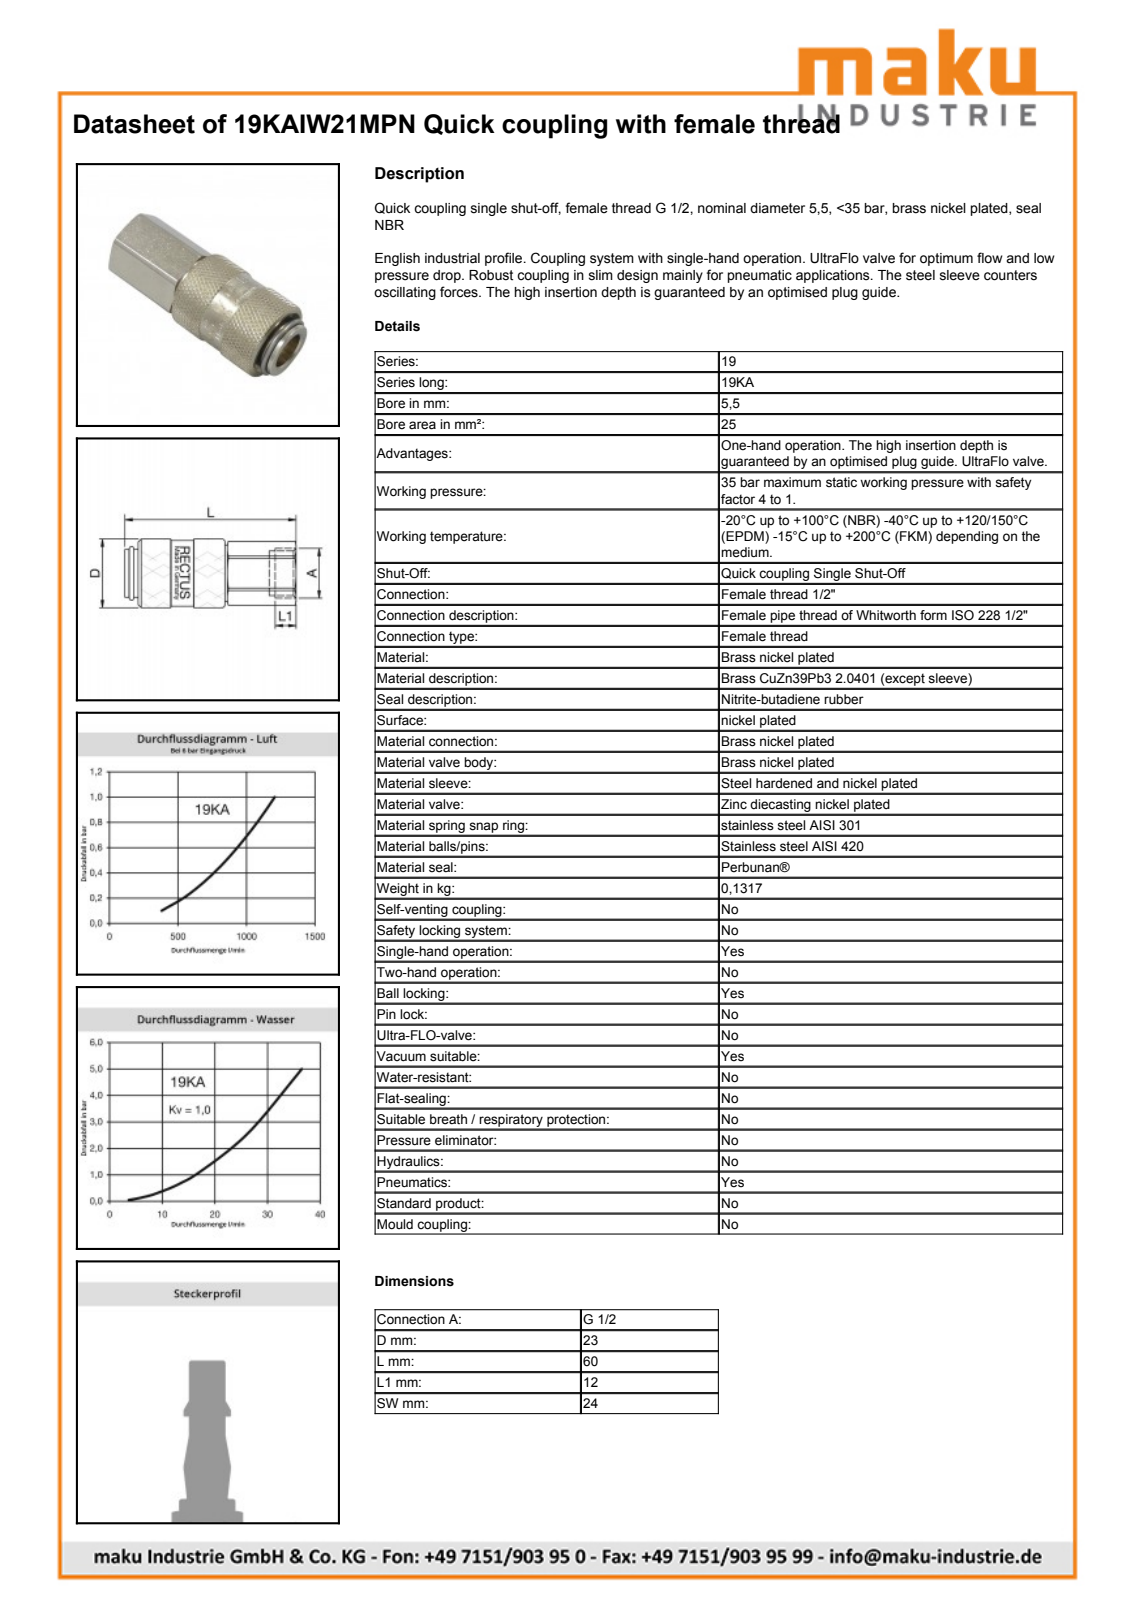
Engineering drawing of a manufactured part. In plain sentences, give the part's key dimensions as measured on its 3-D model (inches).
The part is named "D108866". Its 3-D file was written by "Autodesk Inventor 2013 (AUTOMOTIVE_DESIGN)". It is 1 solid with 321 faces: 129 planar, 41 cylindrical and 151 other. Overall it measures 2.375 by 1.041 by 1.038 inches. Its volume is 1.321 cubic inches and its surface area 14.37 square inches. Round holes: 1 of diameter 0.642, 1 of diameter 0.733, 1 of diameter 0.748, 1 of diameter 0.76, 1 of diameter 0.827. Round bosses or shafts: 1 of diameter 0.906, 1 of diameter 0.866, 1 of diameter 0.746, 1 of diameter 0.708, 1 of diameter 0.63, 1 of diameter 0.591. Partial cylindrical surfaces (rounded edges, fillets, slot ends): 1 of radius 0.429, 1 of radius 0.533. The main face-to-face distances are 0.945, 1.903, 0.553, 1.35, 0.472, 1.026, 2.375, 0.118, 0.176, 0.512.
